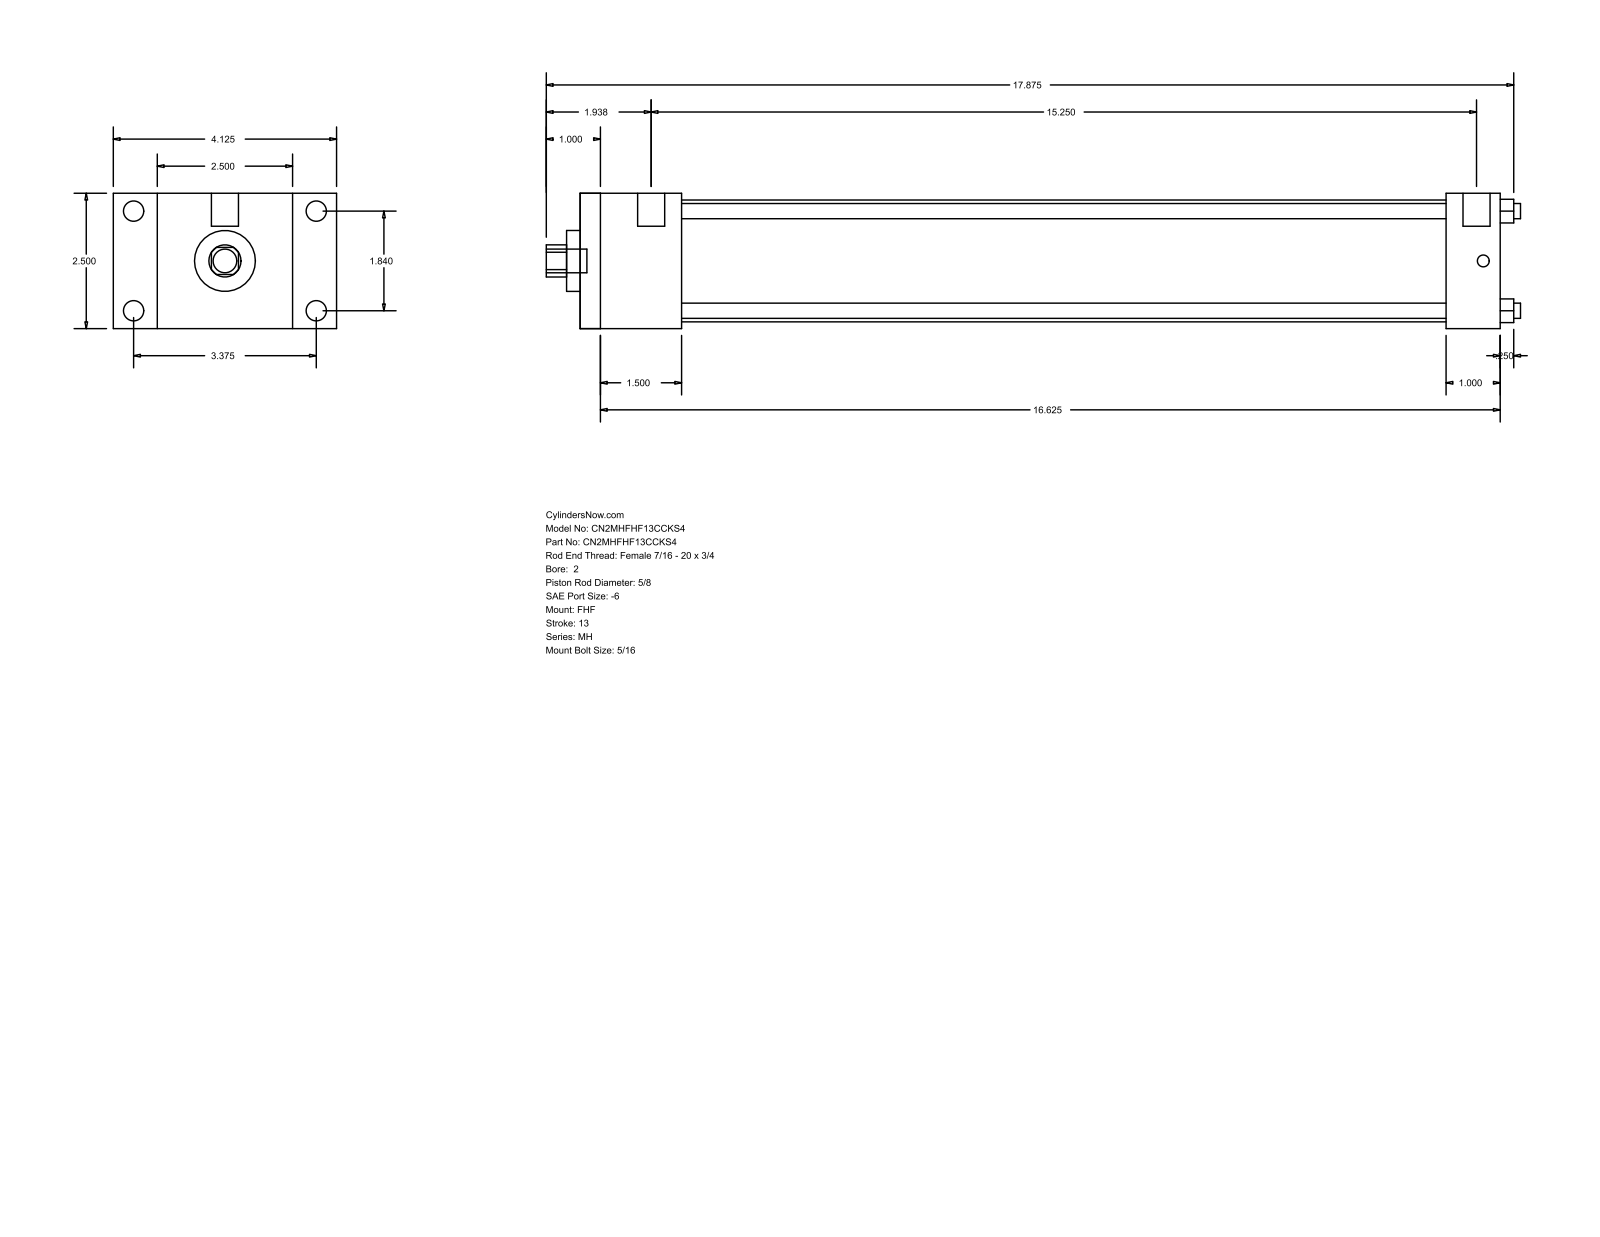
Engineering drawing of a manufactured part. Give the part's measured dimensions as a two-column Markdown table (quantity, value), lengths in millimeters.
| quantity | value |
| --- | --- |
| part name | MH_FHF__0200_0.625 |
| STEP written by | GSSL Pune (CONFIG_CONTROL_DESIGN) |
| units | millimeters |
| bodies | 0 solids, 88 faces (60 planar, 28 cylindrical, 0 other) |
| overall size | 457.2 × 104.78 × 63.5 |
| round holes (diameter × count) | 7.14 × 4, 15.88 × 1, 28.57 × 1, 57.15 × 1 |
| round bosses / shafts (diameter × count) | 9.53 × 4, 5.56 × 4, 12.7 × 2, 11.11 × 1 |
| partial cylindrical surfaces (radius × count) | 7.54 × 1 |
| main face-to-face distances | 63.5, 47.62, 431.8, 384.18, 20.64, 84.14, 104.78, 406.39, 358.77, 25.41 |
| hole center spacings | 33.05, 46.74, 66.1 |
